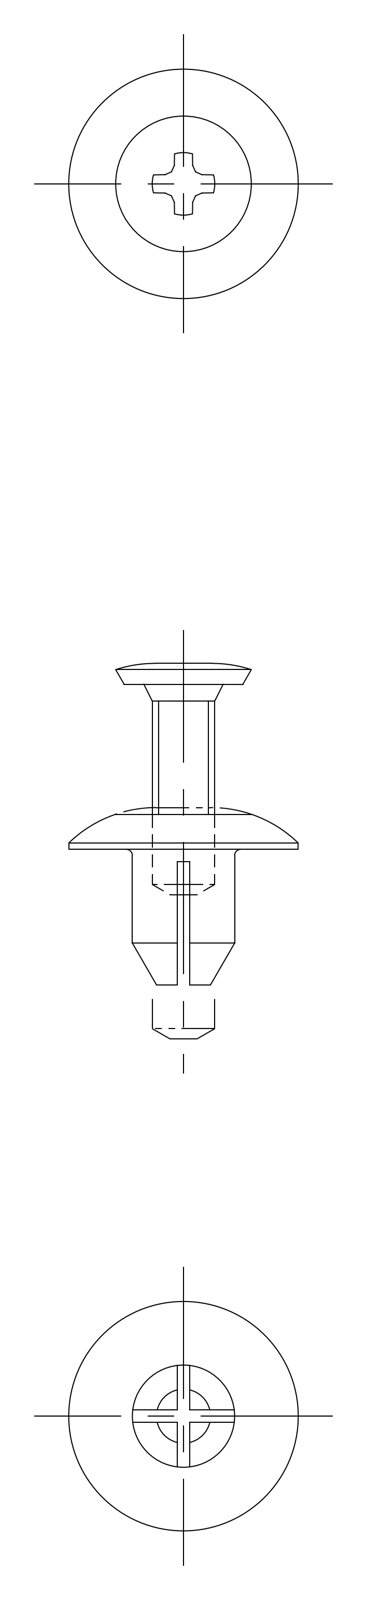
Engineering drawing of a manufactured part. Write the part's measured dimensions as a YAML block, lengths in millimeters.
part_name: "pin; grommet; TL_330_1_9957_36"
step_written_by: "CADfix (AUTOMOTIVE_DESIGN)"
units: millimeters
bodies: {solids: 2, faces: 78, planar: 0, cylindrical: 0, other: 78}
overall_size: [15.41, 11, 11]
volume: 245
surface_area: 543
